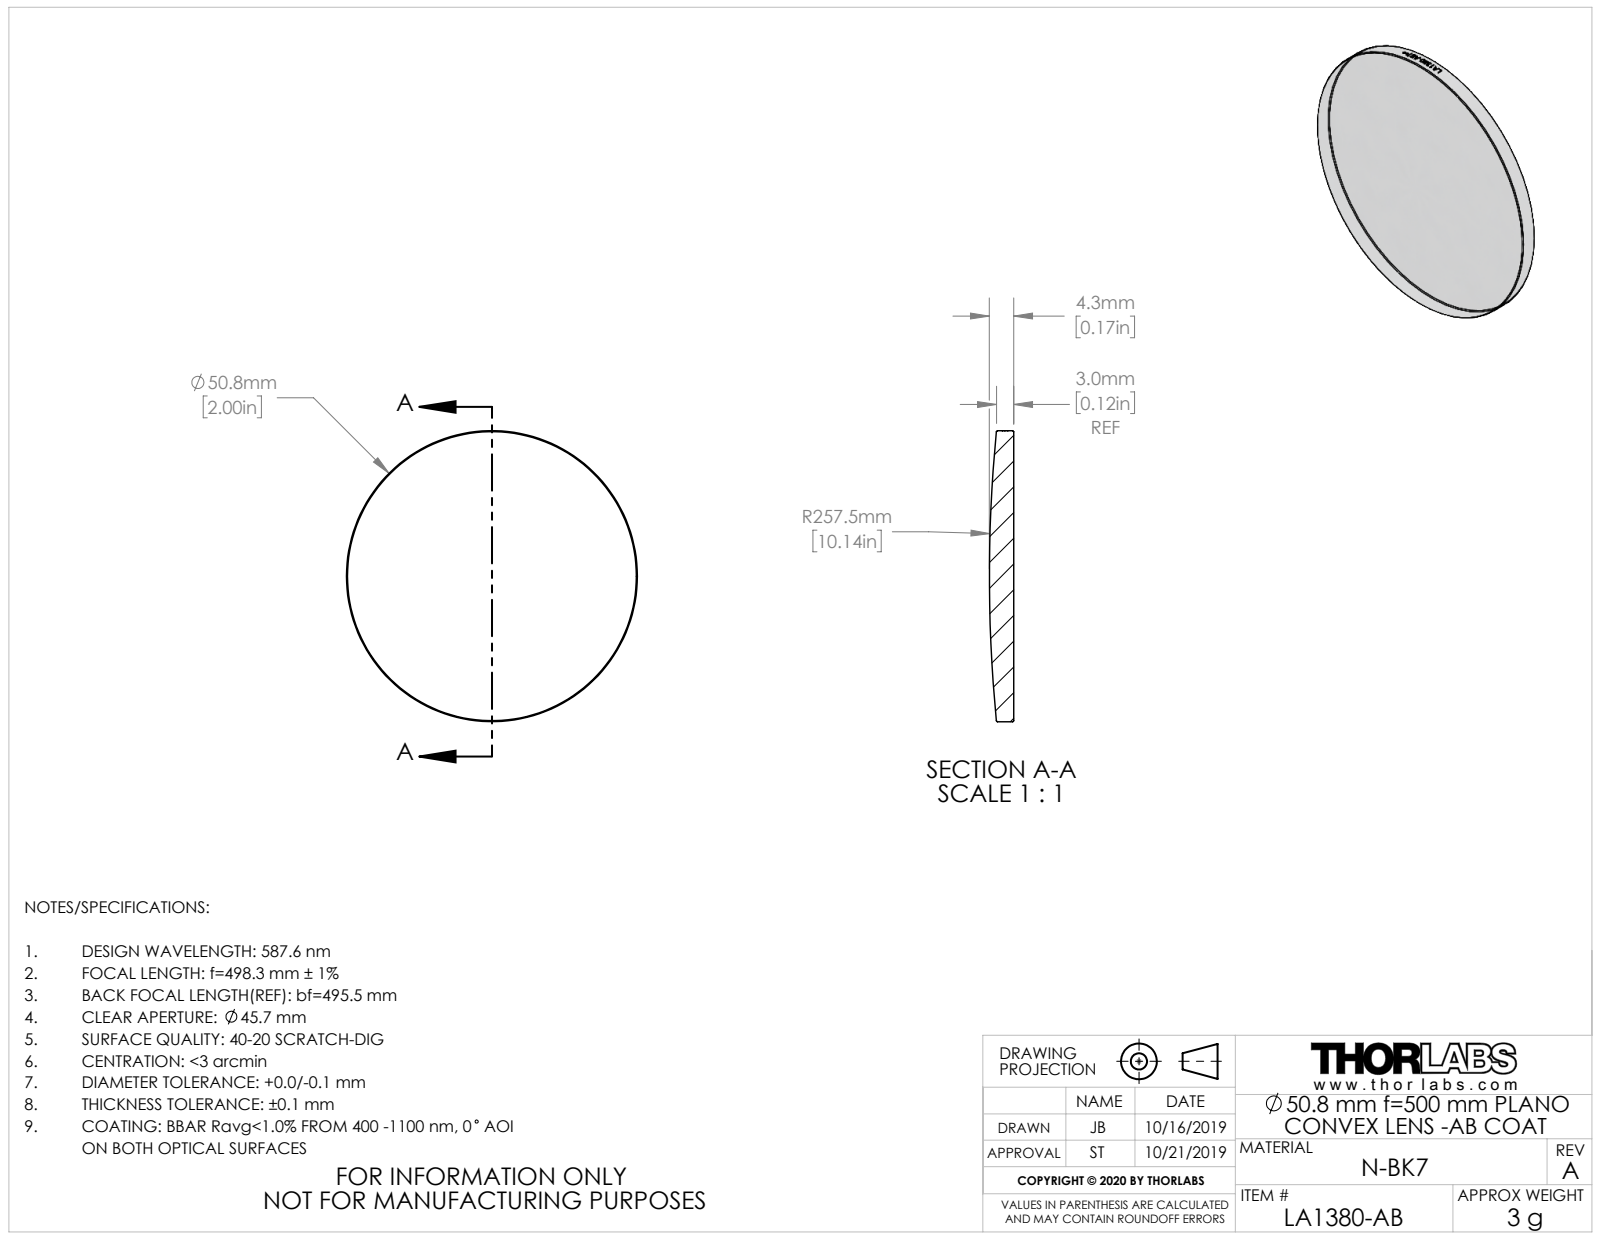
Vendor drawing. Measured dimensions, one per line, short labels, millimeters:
name: TTN195805-E0W
written by: SolidWorks 2018 (CONFIG_CONTROL_DESIGN)
unit: mm
bodies: 1 solid, 29 faces (1 planar, 22 cylindrical, 6 other)
size: 50.8 × 50.8 × 4.25
volume: 7 338 mm³; area: 4 506 mm²
bosses: 1× ⌀50.8
